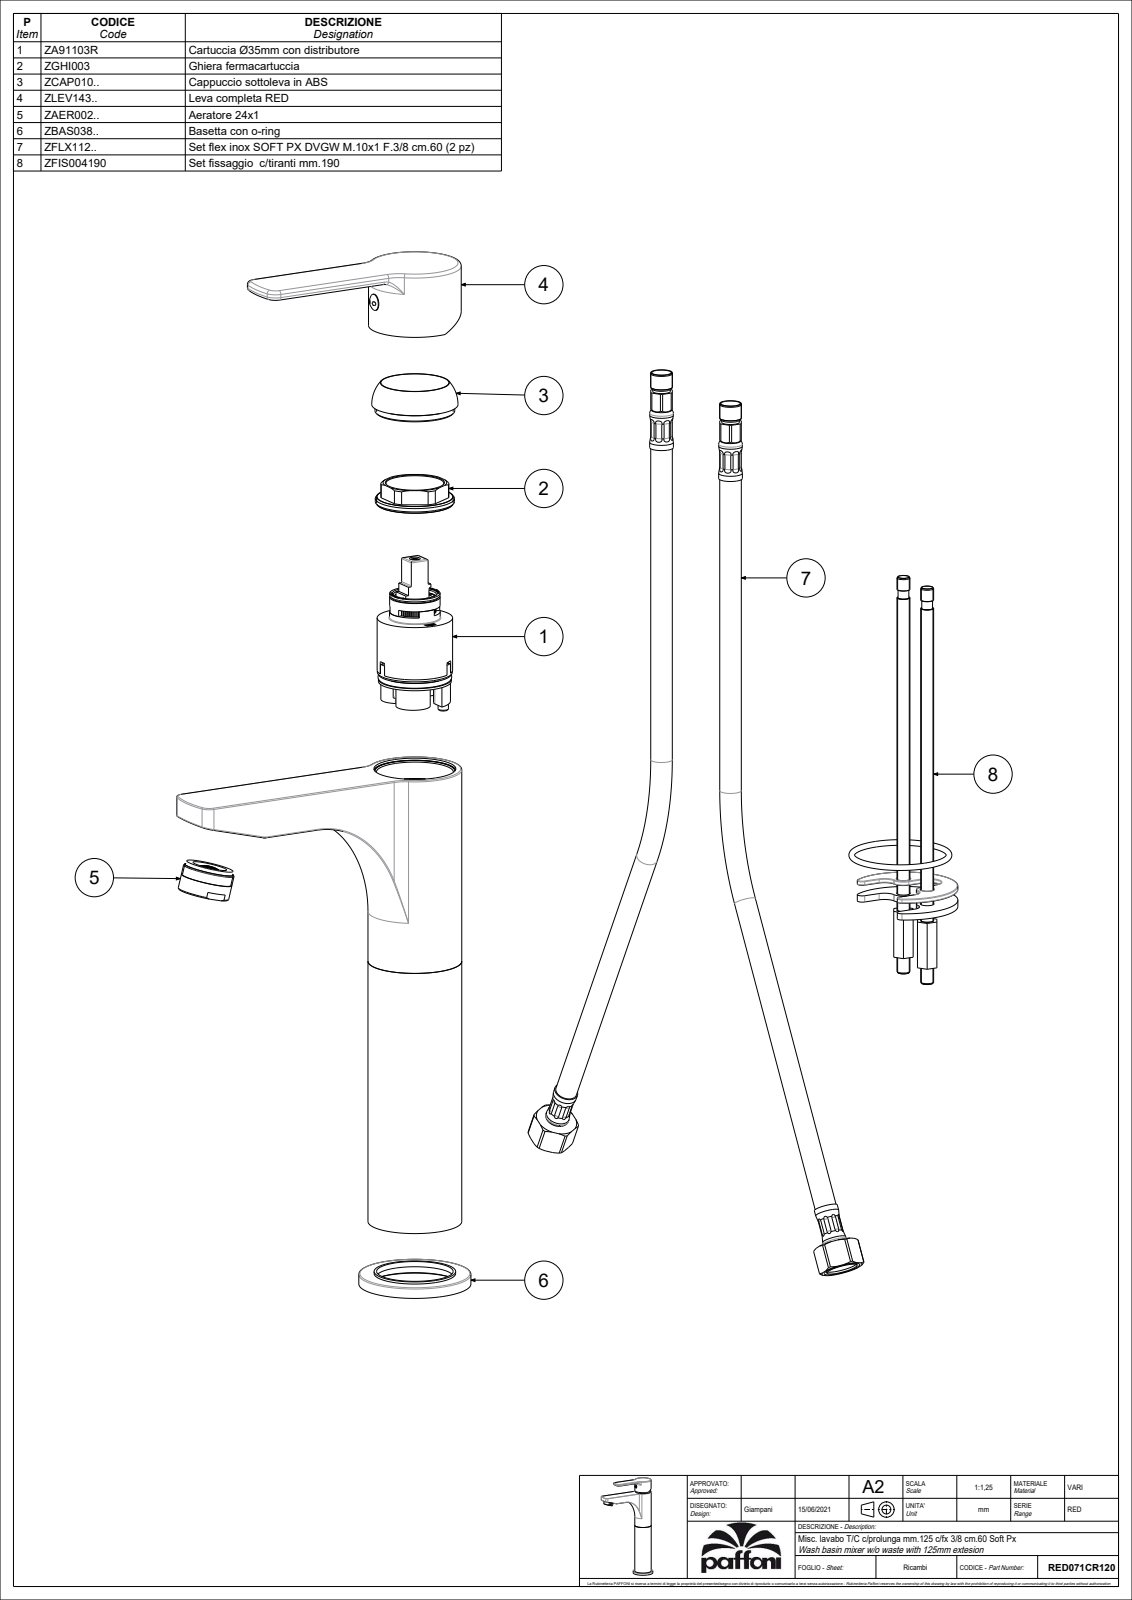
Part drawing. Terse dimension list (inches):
name: RED071CR120
written by: CREO PARAMETRIC BY PTC INC, 2020044 (CONFIG_CONTROL_DESIGN)
unit: in
bodies: 2 solids, 2892 faces (2105 planar, 453 cylindrical, 334 other)
size: 10.068 × 5.846 × 2.047
volume: 10.85 in³; area: 193.3 in²
holes: 5× ⌀0.354, 3× ⌀0.197, 3× ⌀0.472, 2× ⌀0.13, 2× ⌀0.157, 2× ⌀0.217, 2× ⌀0.236, 2× ⌀0.315, 2× ⌀0.433, 1× ⌀0.118, 1× ⌀0.138, 1× ⌀0.177
bosses: 2× ⌀0.189, 1× ⌀2.047, 1× ⌀1.752, 1× ⌀1.713, 1× ⌀1.693, 1× ⌀1.677, 1× ⌀1.516, 1× ⌀1.488
rounds: 88× R0.02, 26× R0.039, 11× R0.006, 9× R0.012, 4× R0.059, 4× R0.197, 4× R0.276, 4× R0.394
face distances: 0.138, 1.083, 1.102, 1.24, 1.22, 1.28, 0.177, 1.417, 0.61, 0.945
hole spacings: 0.535, 0.028, 0.111, 0.335, 0.339, 0.38, 0.388, 0.44
